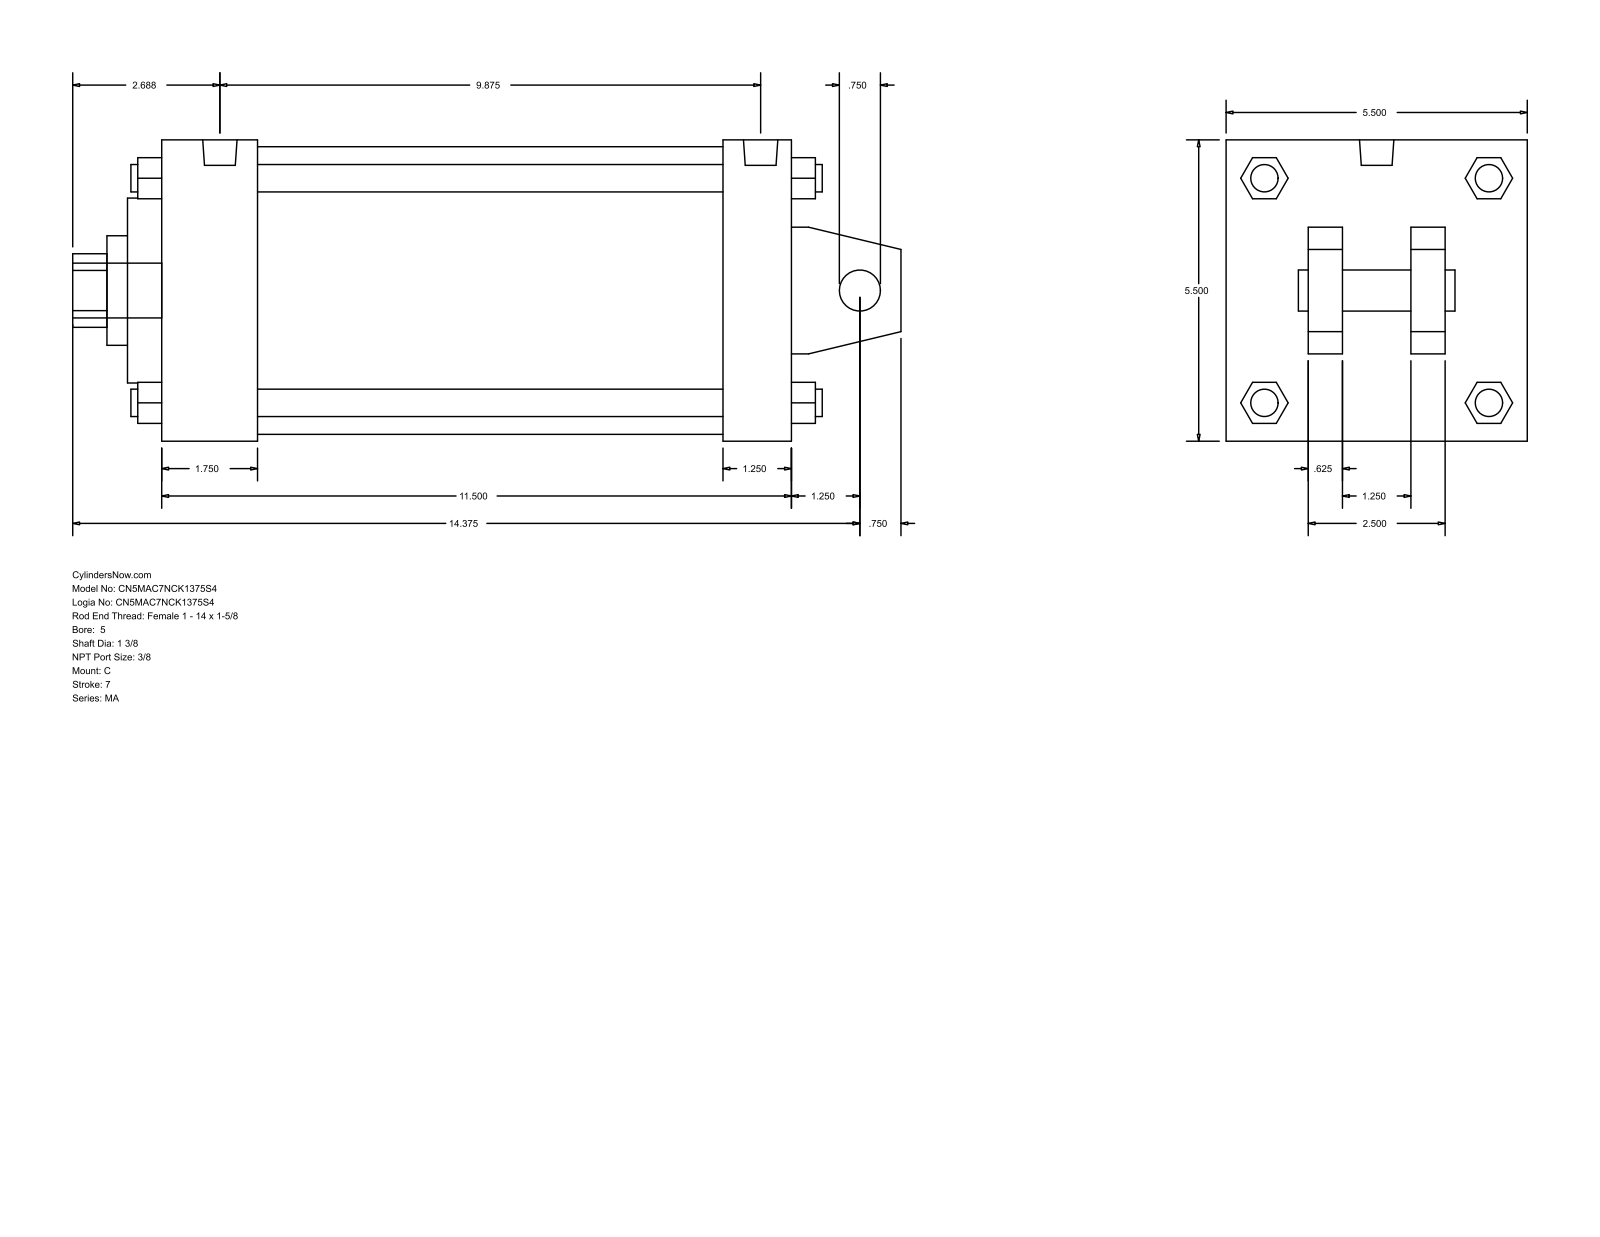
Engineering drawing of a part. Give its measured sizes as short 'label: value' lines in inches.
name: MA_C__0500_1.375
written by: GSSL Pune (CONFIG_CONTROL_DESIGN)
unit: in
bodies: 0 solids, 141 faces (109 planar, 32 cylindrical, 0 other)
size: 15.125 × 5.5 × 5.5
holes: 1× ⌀0.75, 1× ⌀1.375, 1× ⌀2, 1× ⌀3.375, 1× ⌀5.25
bosses: 4× ⌀0.5, 4× ⌀0.437, 2× ⌀0.627, 1× ⌀1
rounds: 1× R0.672
face distances: 5.5, 11.5, 0.625, 1.25, 10.25, 1.75, 8.5, 9.75, 1.5, 4
